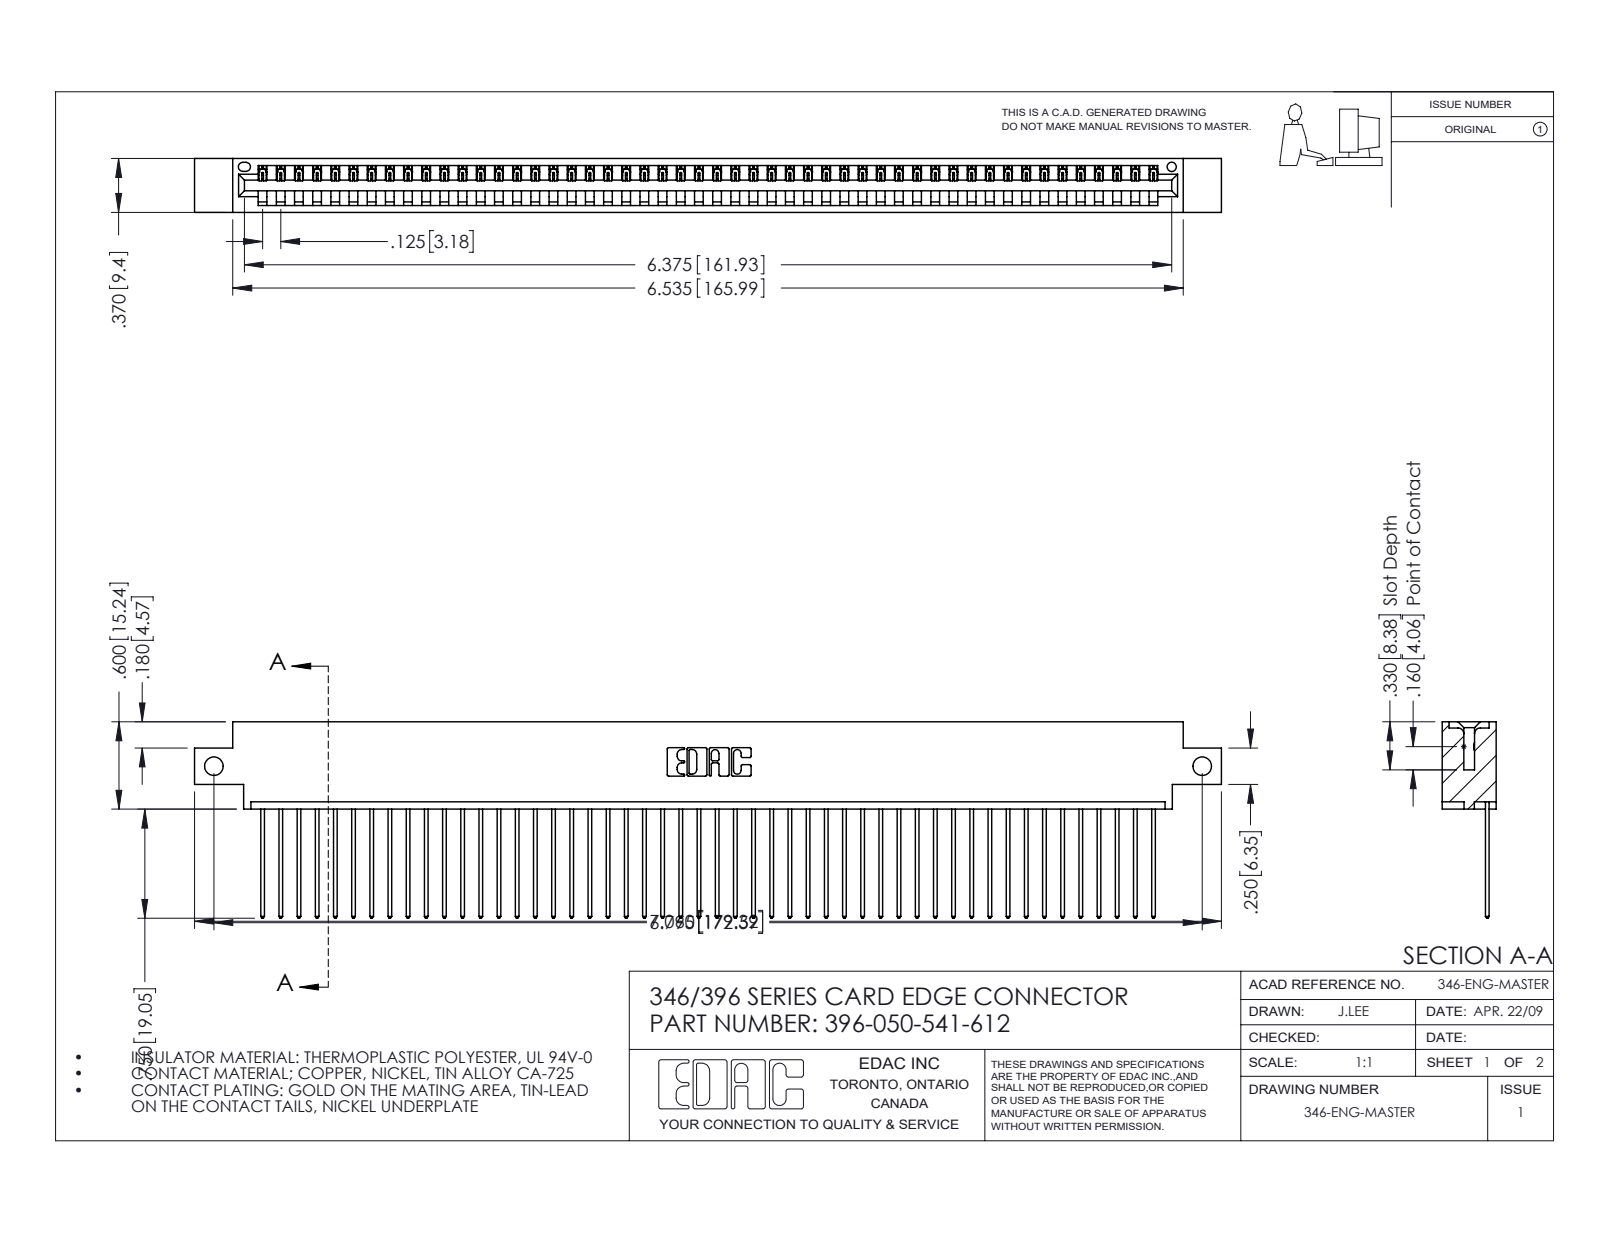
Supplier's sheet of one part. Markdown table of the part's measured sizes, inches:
| quantity | value |
| --- | --- |
| part name | 345-292-001_345-293-141; 346 Part_0.170 Offset - Side Mount; 396-050-541-612 |
| STEP written by | SolidWorks 2016 (CONFIG_CONTROL_DESIGN) |
| units | inches |
| bodies | 51 solids, 3026 faces (2080 planar, 946 cylindrical, 0 other) |
| overall size | 7.06 × 1.35 × 0.37 |
| volume | 1.046 in³ |
| surface area | 34.9 in² |
| round holes (diameter × count) | 0.128 × 2, 0.064 × 1 |
| partial cylindrical surfaces (radius × count) | 0.006 × 100, 0.01 × 100, 0.01 × 22, 0.007 × 6, 0.031 × 6, 0.026 × 3, 0.031 × 2, 0.04 × 2 |
| main face-to-face distances | 0.048, 0.322, 0.37, 0.25, 0.072, 0.298, 0.025, 0.148, 0.222, 0.1 |
| hole center spacings | 6.795 |
